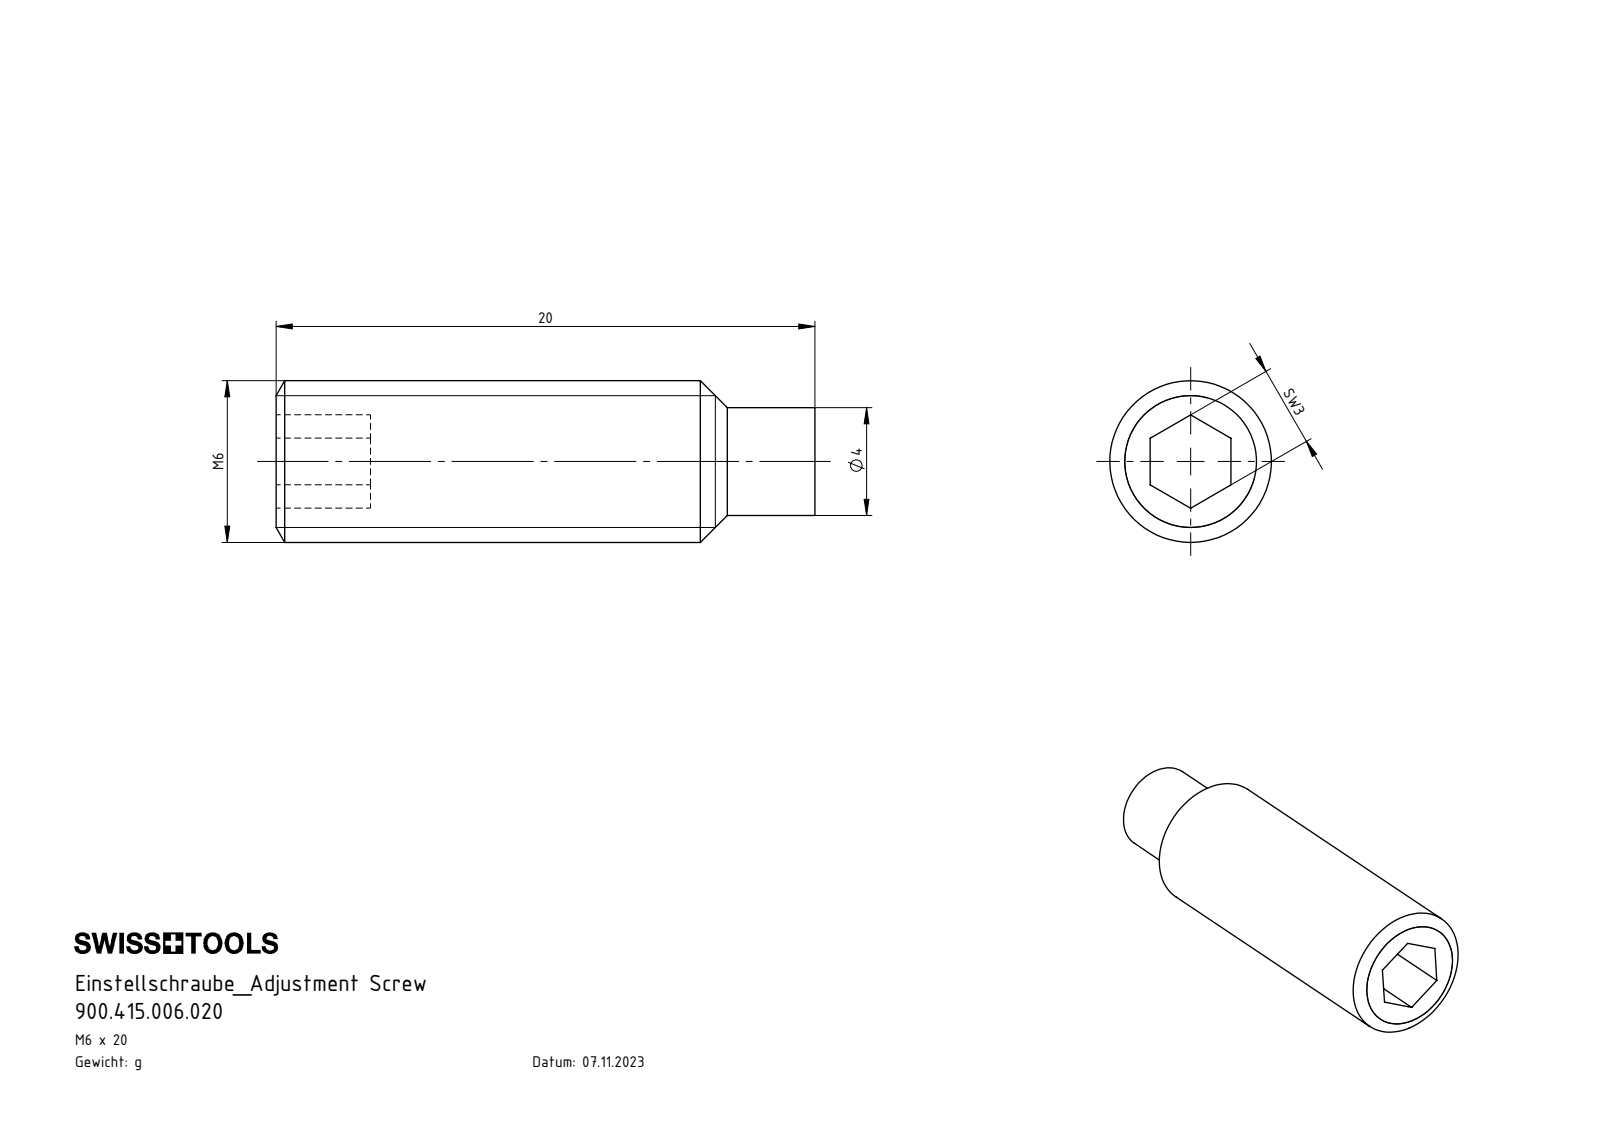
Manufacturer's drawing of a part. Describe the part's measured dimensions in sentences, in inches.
The part is named "900.415.006.020". Its 3-D file was written by "SolidWorks 2022 (AUTOMOTIVE_DESIGN)". It is 1 solid with 17 faces: 9 planar, 4 cylindrical and 4 other. Overall it measures 0.787 by 0.236 by 0.236 inches. Its volume is 0.029 cubic inches and its surface area 0.671 square inches. Round bosses or shafts: 1 of diameter 0.236, 1 of diameter 0.157. The main face-to-face distances are 0.118, 0.787, 0.138, 0.65.
